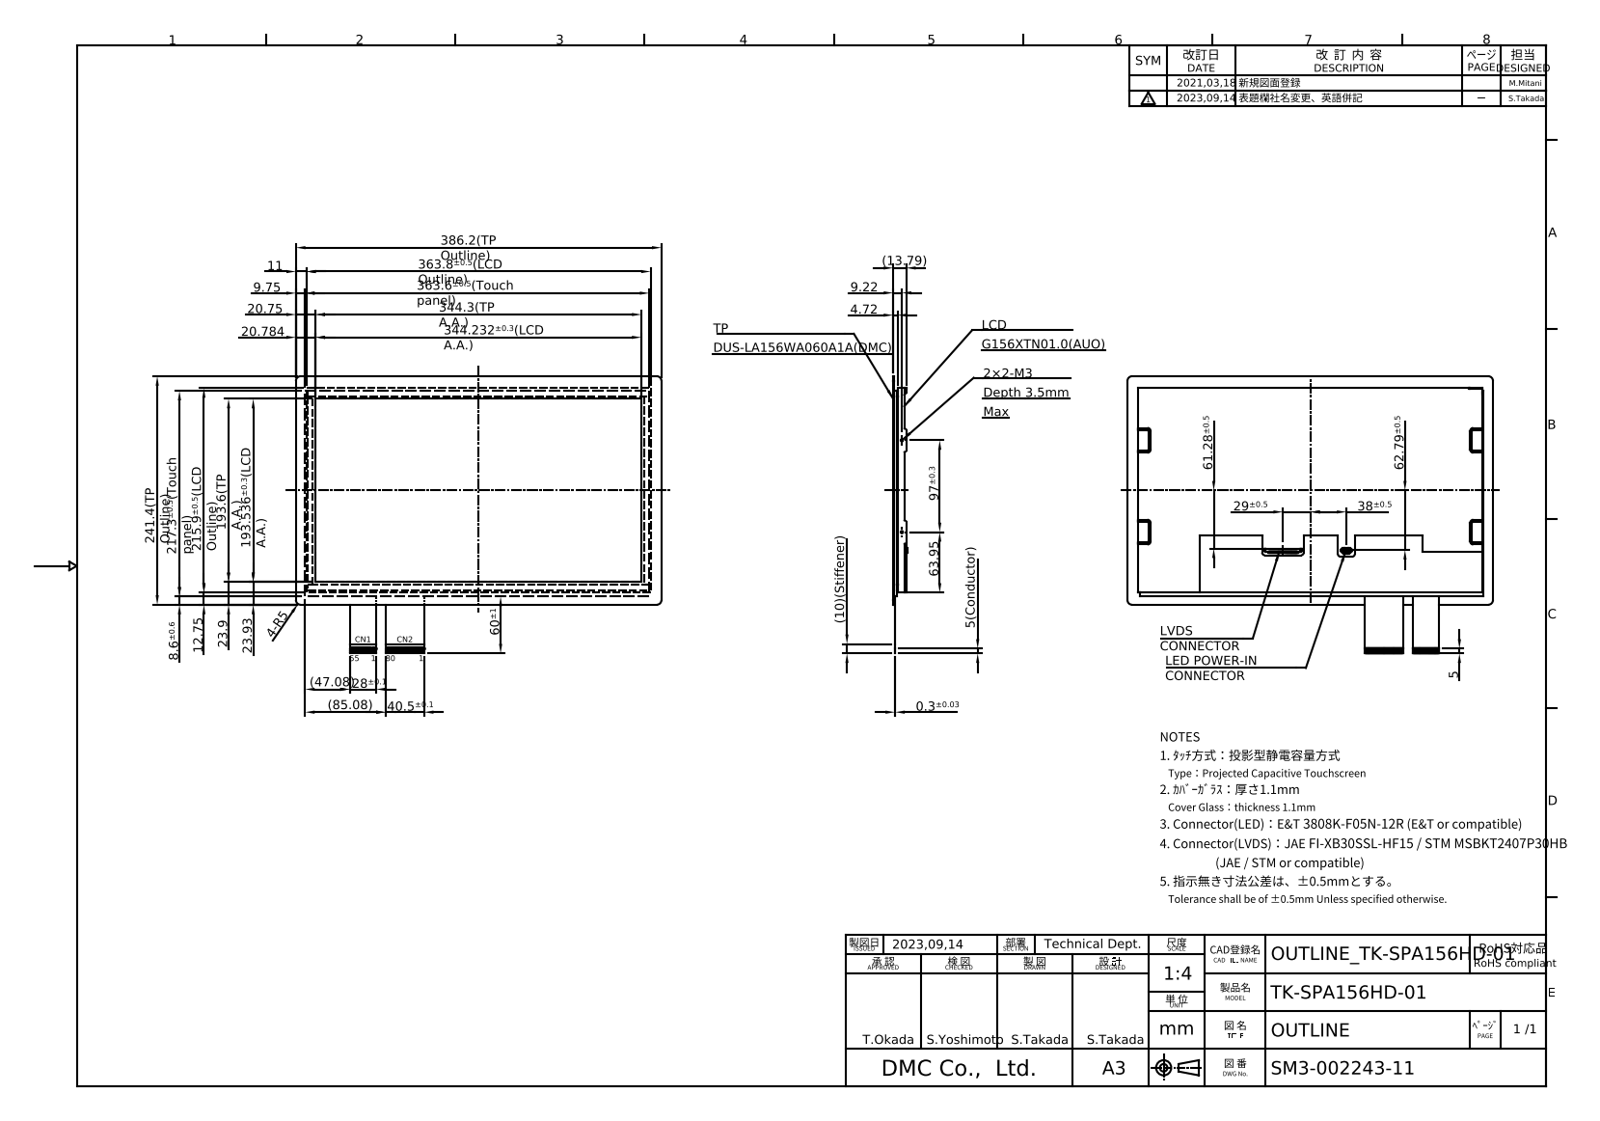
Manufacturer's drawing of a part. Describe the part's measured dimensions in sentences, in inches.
The part is named "HP_TK-SPA156HD-01". Its 3-D file was written by "Autodesk Inventor 2020 (AUTOMOTIVE_DESIGN)". It is 1 solid with 2719 faces: 2325 planar, 362 cylindrical and 32 other. Overall it measures 15.205 by 11.528 by 0.598 inches. Its volume is 54.7 cubic inches and its surface area 555.8 square inches. Round holes: 2 of diameter 0.097. Partial cylindrical surfaces (rounded edges, fillets, slot ends): 21 of radius 0.004, 14 of radius 0.008, 12 of radius 0.039, 11 of radius 0.01, 4 of radius 0.118, 4 of radius 0.197, 3 of radius 0.006, 2 of radius 0.014. The main face-to-face distances are 0.142, 0.044, 0.186, 0.464, 0.278, 0.322, 0.079, 0.357, 0.401, 0.543. The hole center spacings are 3.819.
